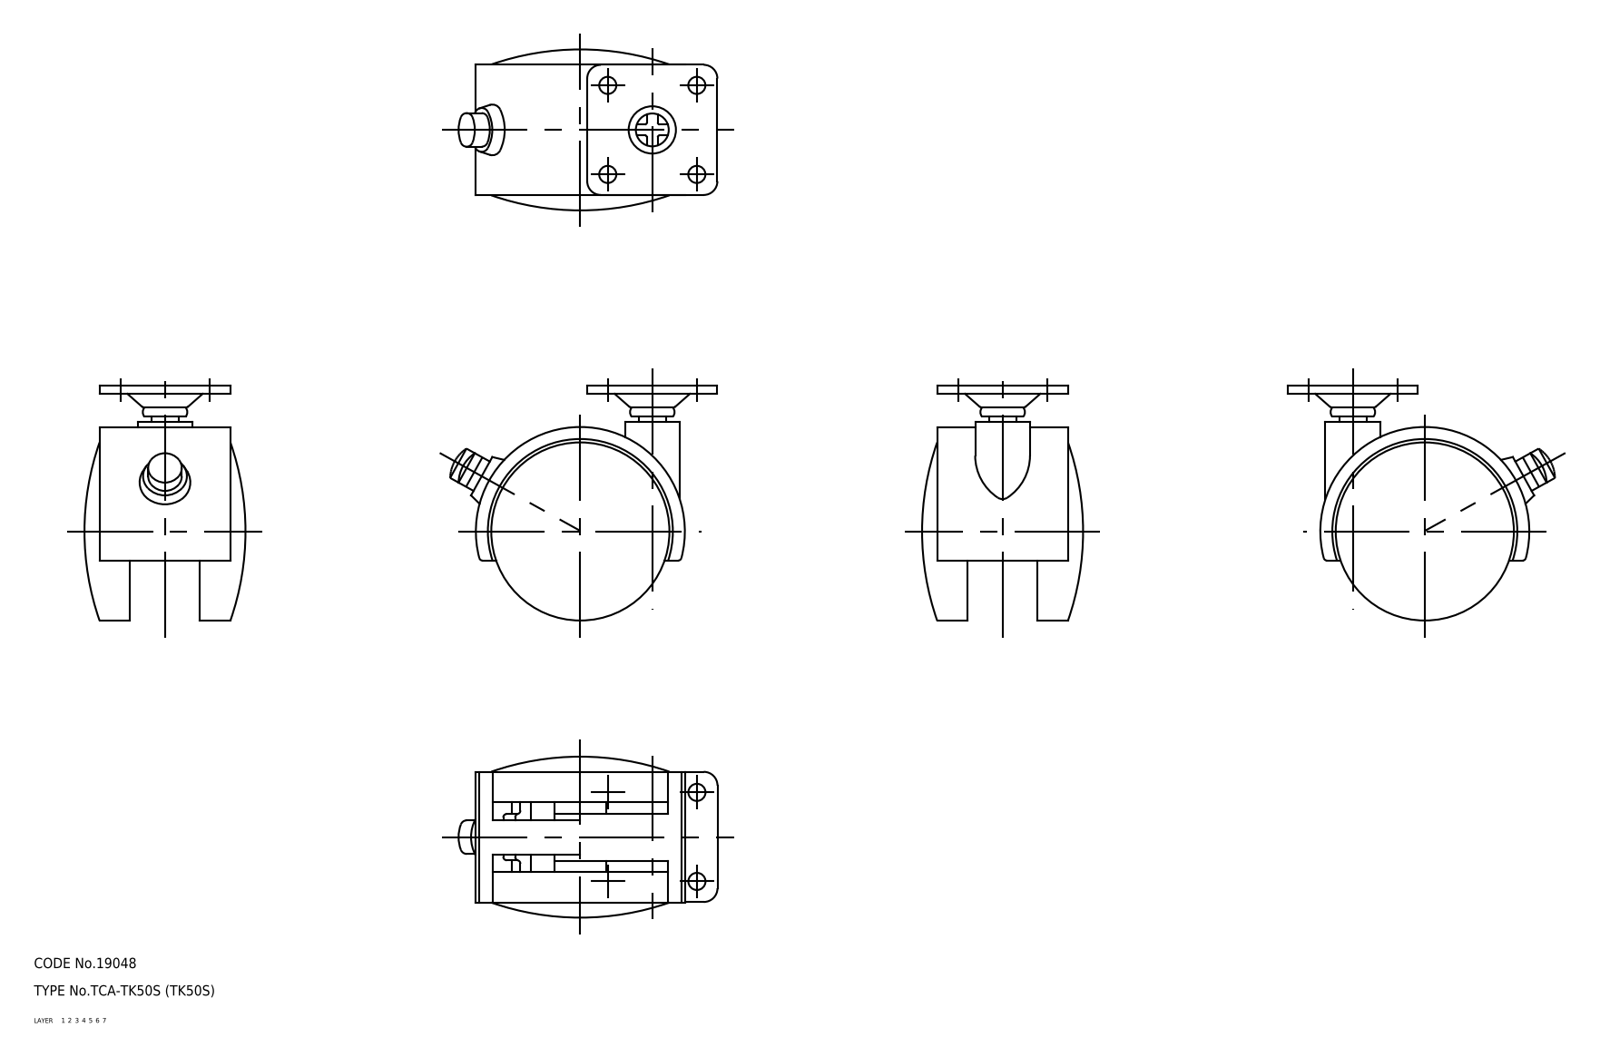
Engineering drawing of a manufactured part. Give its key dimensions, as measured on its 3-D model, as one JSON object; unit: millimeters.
{"part_name": "wheel; mounting plate; main shaft; TK50S_4931_36", "step_written_by": "CADfix (AUTOMOTIVE_DESIGN)", "units": "millimeters", "bodies": {"solids": 5, "faces": 141, "planar": 0, "cylindrical": 0, "other": 141}, "overall_size": [75.55, 68.5, 47], "volume_mm3": 73878, "surface_area_mm2": 33581}
